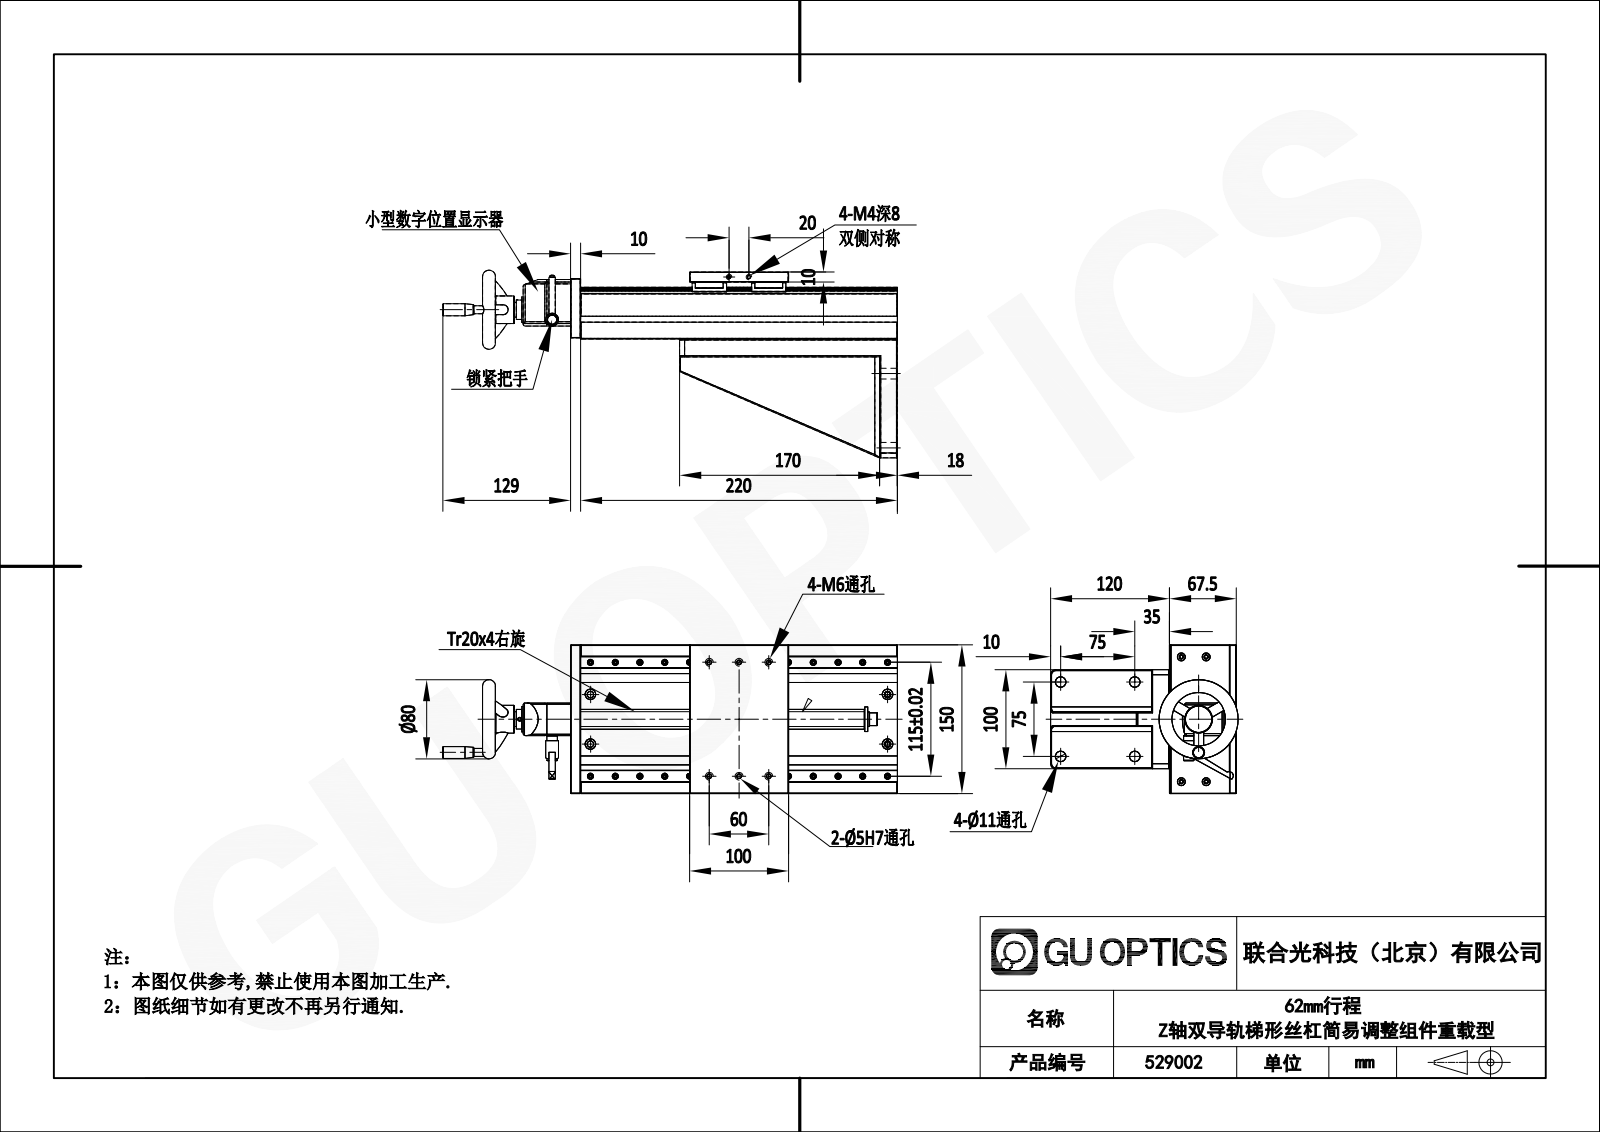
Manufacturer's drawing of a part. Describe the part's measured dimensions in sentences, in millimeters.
The part is named "DHQ46-170-C". Its 3-D file was written by "SolidWorks 2023 (CONFIG_CONTROL_DESIGN)". It is 0 solids with 715 faces: 261 planar, 380 cylindrical and 74 other. Overall it measures 321.5 by 192.5 by 150 millimeters. Round holes: 16 of diameter 6.5, 15 of diameter 5, 10 of diameter 6, 10 of diameter 11, 5 of diameter 10, 4 of diameter 8, 3 of diameter 4.92, 3 of diameter 4.92, 2 of diameter 2.5, 2 of diameter 3.3, 2 of diameter 4. Round bosses or shafts: 1 of diameter 27, 1 of diameter 24, 1 of diameter 20, 1 of diameter 19.8, 1 of diameter 15.5, 1 of diameter 14, 1 of diameter 13, 1 of diameter 10.5. Partial cylindrical surfaces (rounded edges, fillets, slot ends): 15 of radius 4.67, 11 of radius 7, 10 of radius 1, 9 of radius 2, 4 of radius 1.32, 4 of radius 5, 2 of radius 3, 1 of radius 0.5. The main face-to-face distances are 10, 57.5, 67.5, 18, 15, 42.5, 28, 82.5, 25, 75.5. The hole center spacings are 25, 115, 135, 20, 32.5, 41, 50, 86.2.
